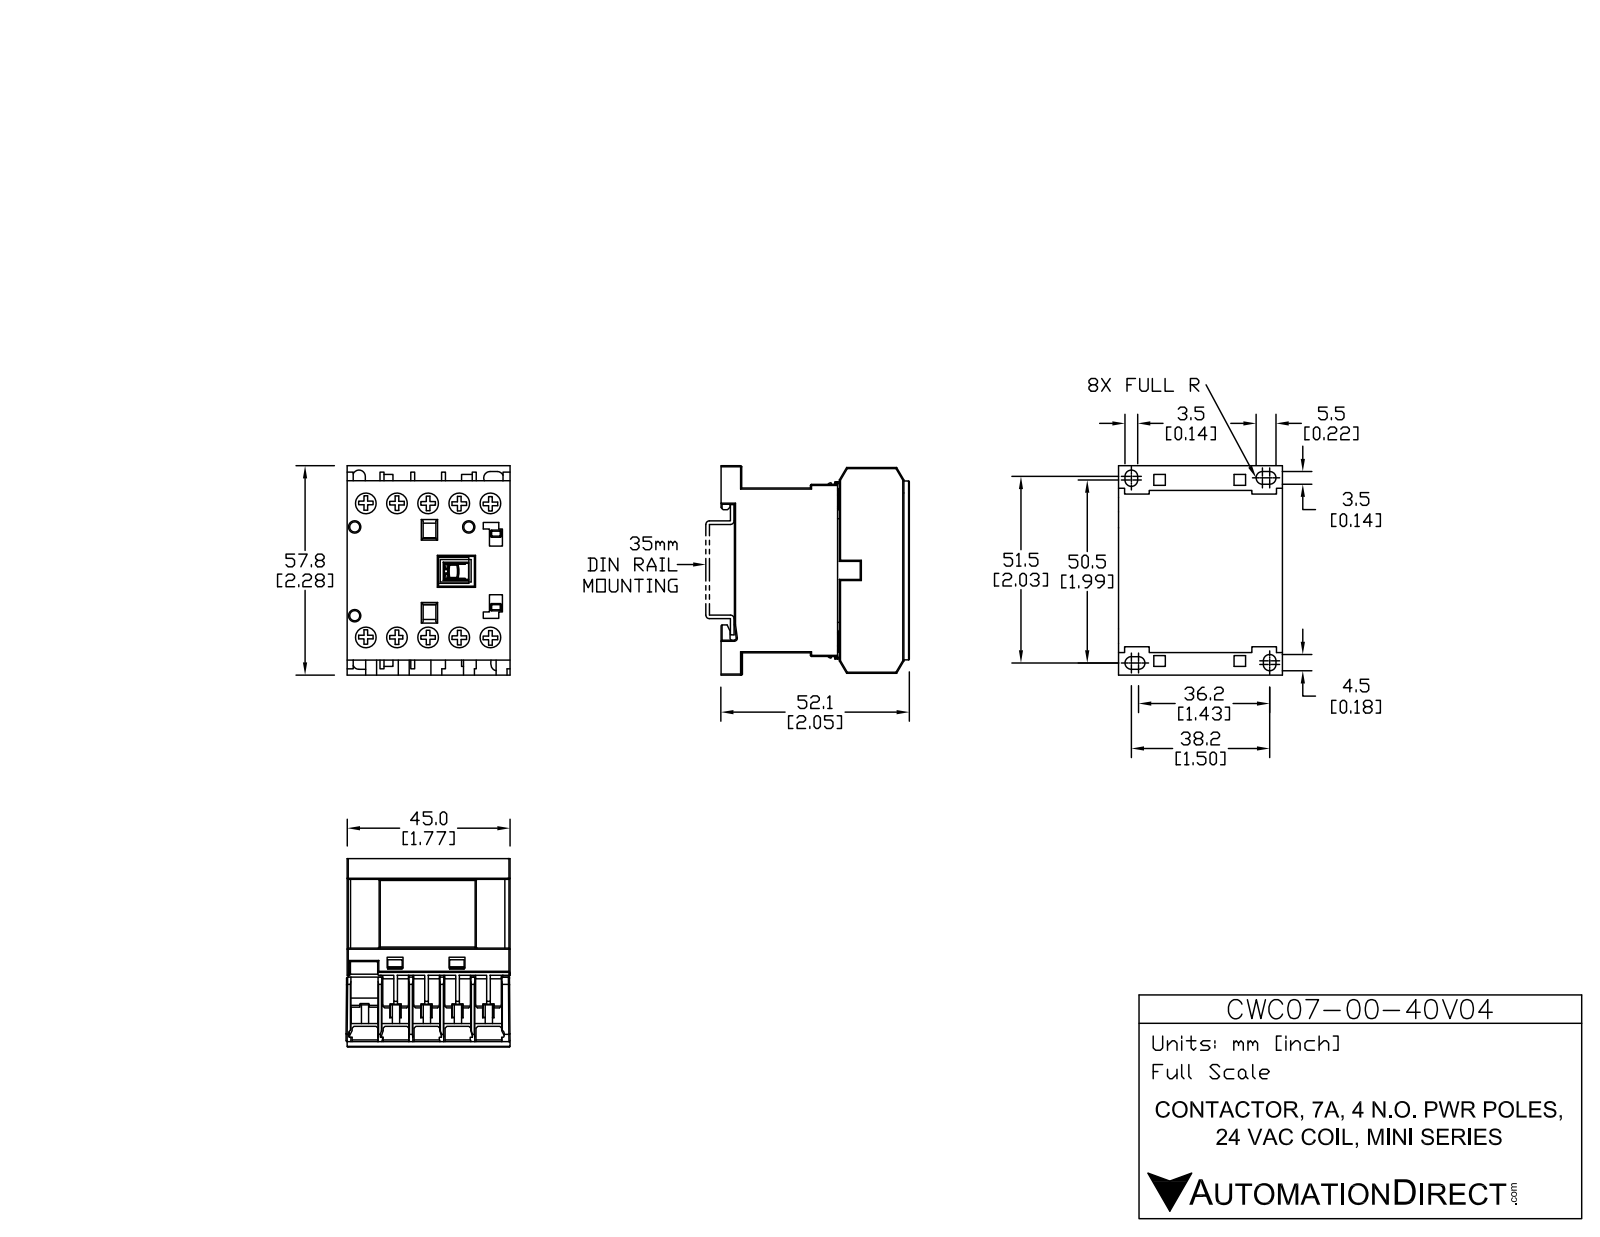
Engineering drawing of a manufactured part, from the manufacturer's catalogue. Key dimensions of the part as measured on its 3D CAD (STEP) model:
Part name (STEP PRODUCT): CWC07-00-40V04
STEP written by: SolidWorks 2013 (AUTOMOTIVE_DESIGN)
Units: millimetres
Bodies: 15 solids, 535 faces (445 planar, 90 cylindrical, 0 other)
Overall size (bounding box): 58.04 × 52.12 × 45.75
Volume: 97 133 mm³ · Surface area: 30 437 mm²
Round holes (diameter × count): ⌀6.2 ×10, ⌀2.8 ×3
Round bosses / shafts (diameter × count): ⌀5.9 ×10
Partial cylindrical surfaces — rounded edges, fillets, slot ends (radius × count): R0.3 ×20, R1.72 ×6, R1.73 ×2, R0.32 ×1, R0.42 ×1, R0.55 ×1
Main face-to-face distances: 8.25, 45.5, 1.25, 16.5, 9.5, 5.5, 17.75, 5.13, 10.63, 7
Hole centre spacings: 8.55, 37.94, 17.1, 40.72, 36.96, 25.65, 44.99, 6.91
